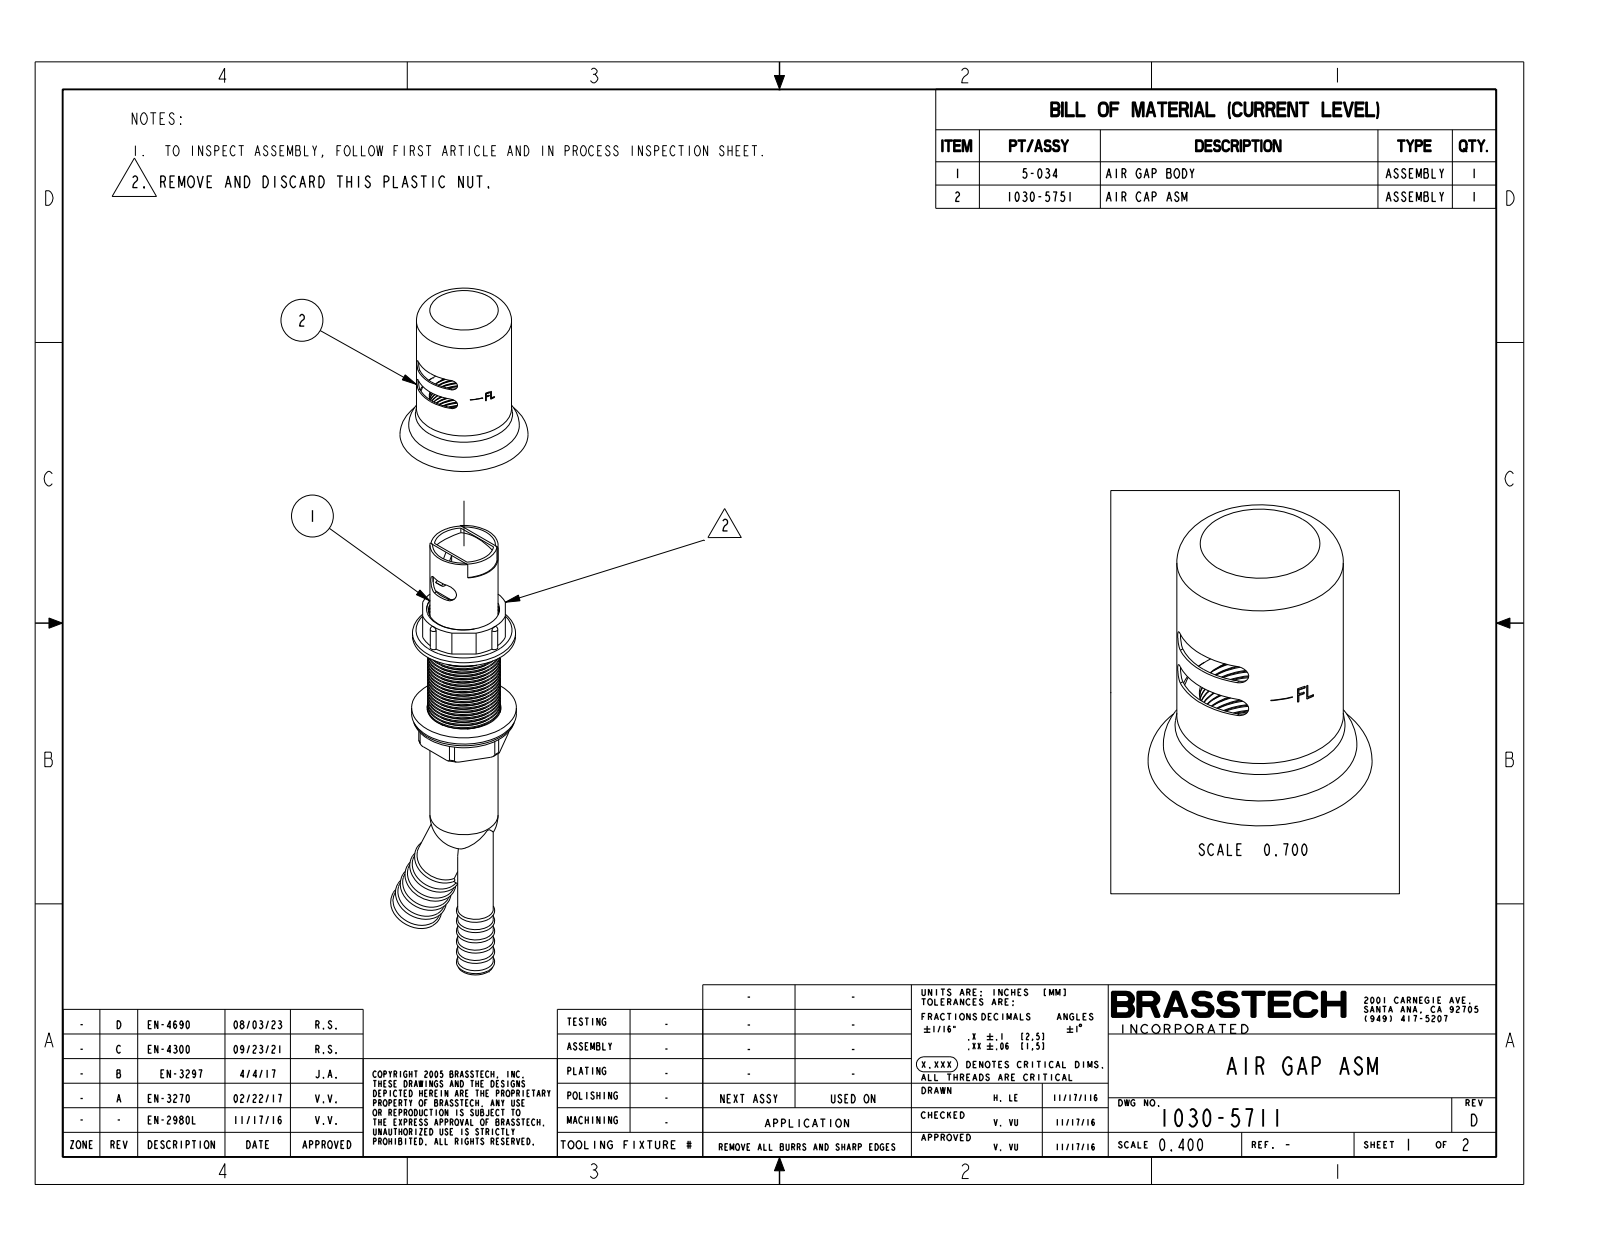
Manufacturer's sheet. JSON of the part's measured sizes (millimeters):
{"part_name": "1030-5711", "step_written_by": "CREO PARAMETRIC BY PTC INC, 2018400 (AUTOMOTIVE_DESIGN)", "units": "millimeters", "bodies": {"solids": 1, "faces": 270, "planar": 67, "cylindrical": 128, "other": 75}, "overall_size": [223.6, 68.1, 55.9], "volume_mm3": 166800, "surface_area_mm2": 51550, "round_holes": [[30.5, 1], [32.3, 1], [32.5, 1], [40, 1]], "round_bosses_or_shafts": [[45.7, 1], [44.7, 1], [42.4, 1], [41.5, 1], [32, 1], [29.7, 1], [21.7, 1], [15.5, 1]], "partial_cylinders_radius": [[1, 6], [2.5, 4], [4, 2], [20.5, 1]], "face_to_face_distances": [23.4, 89, 89.8, 65.7, 66.4, 0.8, 34.3, 11, 54.7, 55.4]}
